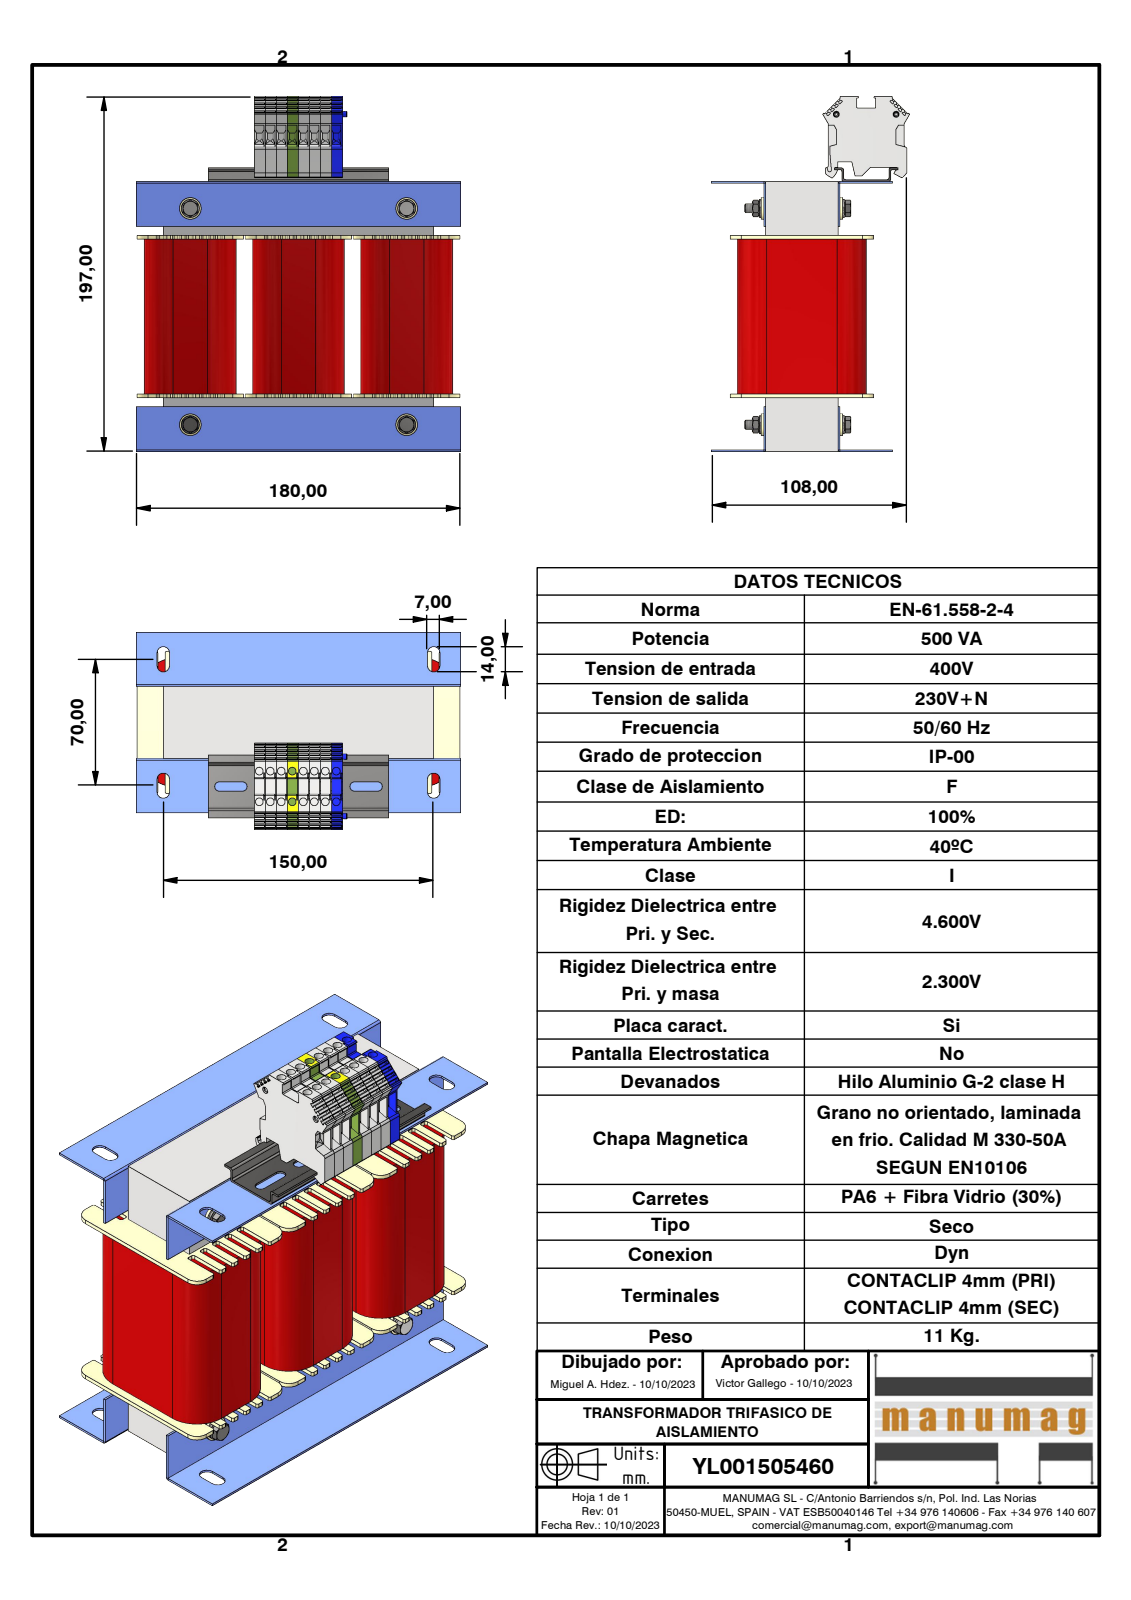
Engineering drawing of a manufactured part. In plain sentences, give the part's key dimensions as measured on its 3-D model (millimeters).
The part is named "YL001505460; 3UI90 150 x 150 - 40 (Rc30); UI 90_40; RC30 NT030 (+8 more)". Its 3-D file was written by "Autodesk Inventor 2023 (AUTOMOTIVE_DESIGN)". It is 41 solids with 3082 faces: 2178 planar, 736 cylindrical and 168 other. Overall it measures 197.25 by 180 by 109.47 millimeters. Its volume is 1 392 000 cubic millimeters and its surface area 347 462 square millimeters. Round holes: 16 of diameter 4.3, 4 of diameter 4.13, 4 of diameter 5, 4 of diameter 5.3, 4 of diameter 6, 4 of diameter 10.5, 2 of diameter 2.4, 2 of diameter 2.5, 2 of diameter 2.75, 2 of diameter 2.95. Round bosses or shafts: 4 of diameter 12, 4 of diameter 10, 4 of diameter 6.7, 4 of diameter 5.9, 4 of diameter 4.57. Partial cylindrical surfaces (rounded edges, fillets, slot ends): 132 of radius 1, 16 of radius 0.25, 12 of radius 6, 12 of radius 16, 8 of radius 2.6, 8 of radius 3.5, 5 of radius 0.3, 5 of radius 0.5. The main face-to-face distances are 30, 1, 60, 120, 40, 90, 150, 119, 29, 10.5. The hole center spacings are 6.1, 18.06, 12.2, 20.92, 18.3, 24.98, 17, 24.4.
